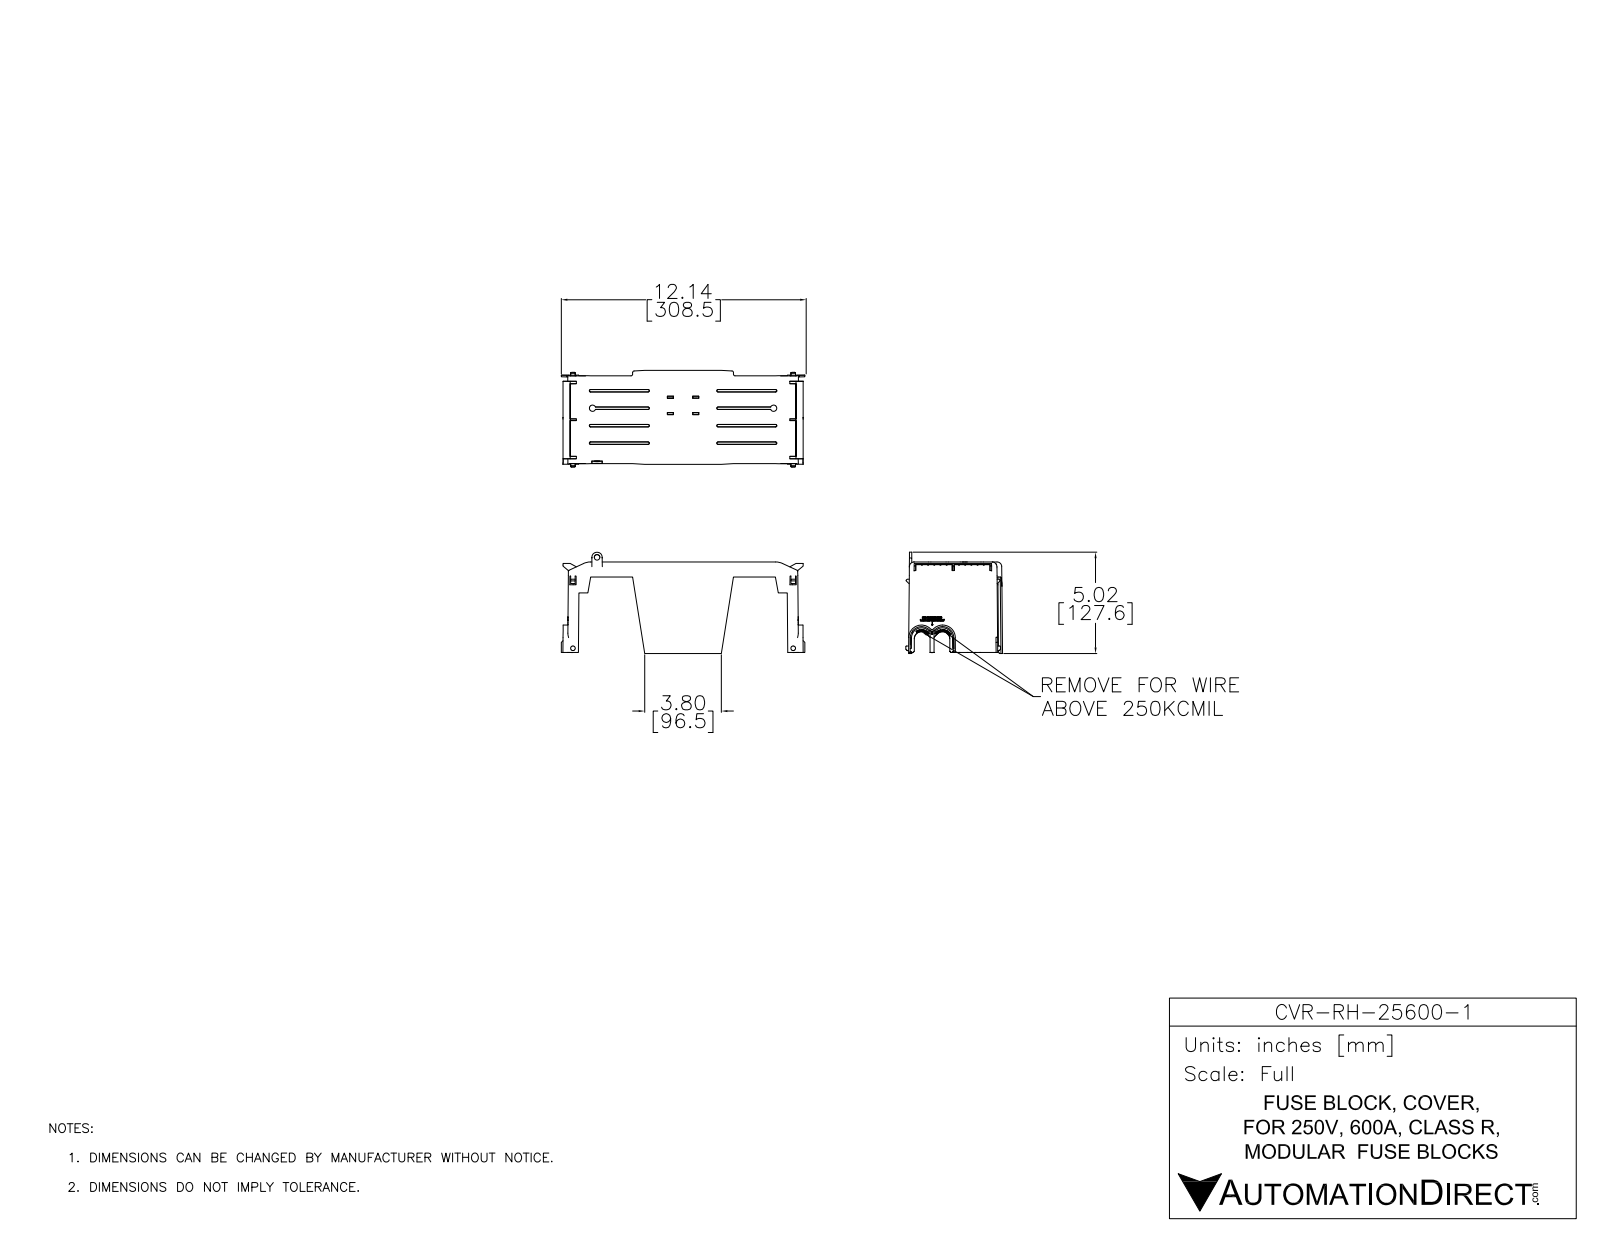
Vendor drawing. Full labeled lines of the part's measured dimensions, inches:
Part name (STEP PRODUCT): CVR-RH-25600-1
STEP written by: SolidWorks 2017 (AUTOMOTIVE_DESIGN)
Units: inches
Bodies: 1 solid, 2344 faces (1576 planar, 119 cylindrical, 649 other)
Overall size (bounding box): 12.076 × 5.026 × 4.796
Volume: 12.93 in³ · Surface area: 333.4 in²
Round holes (diameter × count): ⌀0.276 ×1
Partial cylindrical surfaces — rounded edges, fillets, slot ends (radius × count): R0.039 ×18, R0.157 ×9, R0.118 ×8, R0.236 ×7, R0.079 ×4, R0.354 ×4, R0.492 ×4, R0.551 ×4
Main face-to-face distances: 0.079, 0.236, 0.157, 0.315, 0.197, 0.118, 0.795, 2.52, 0.158, 0.866
